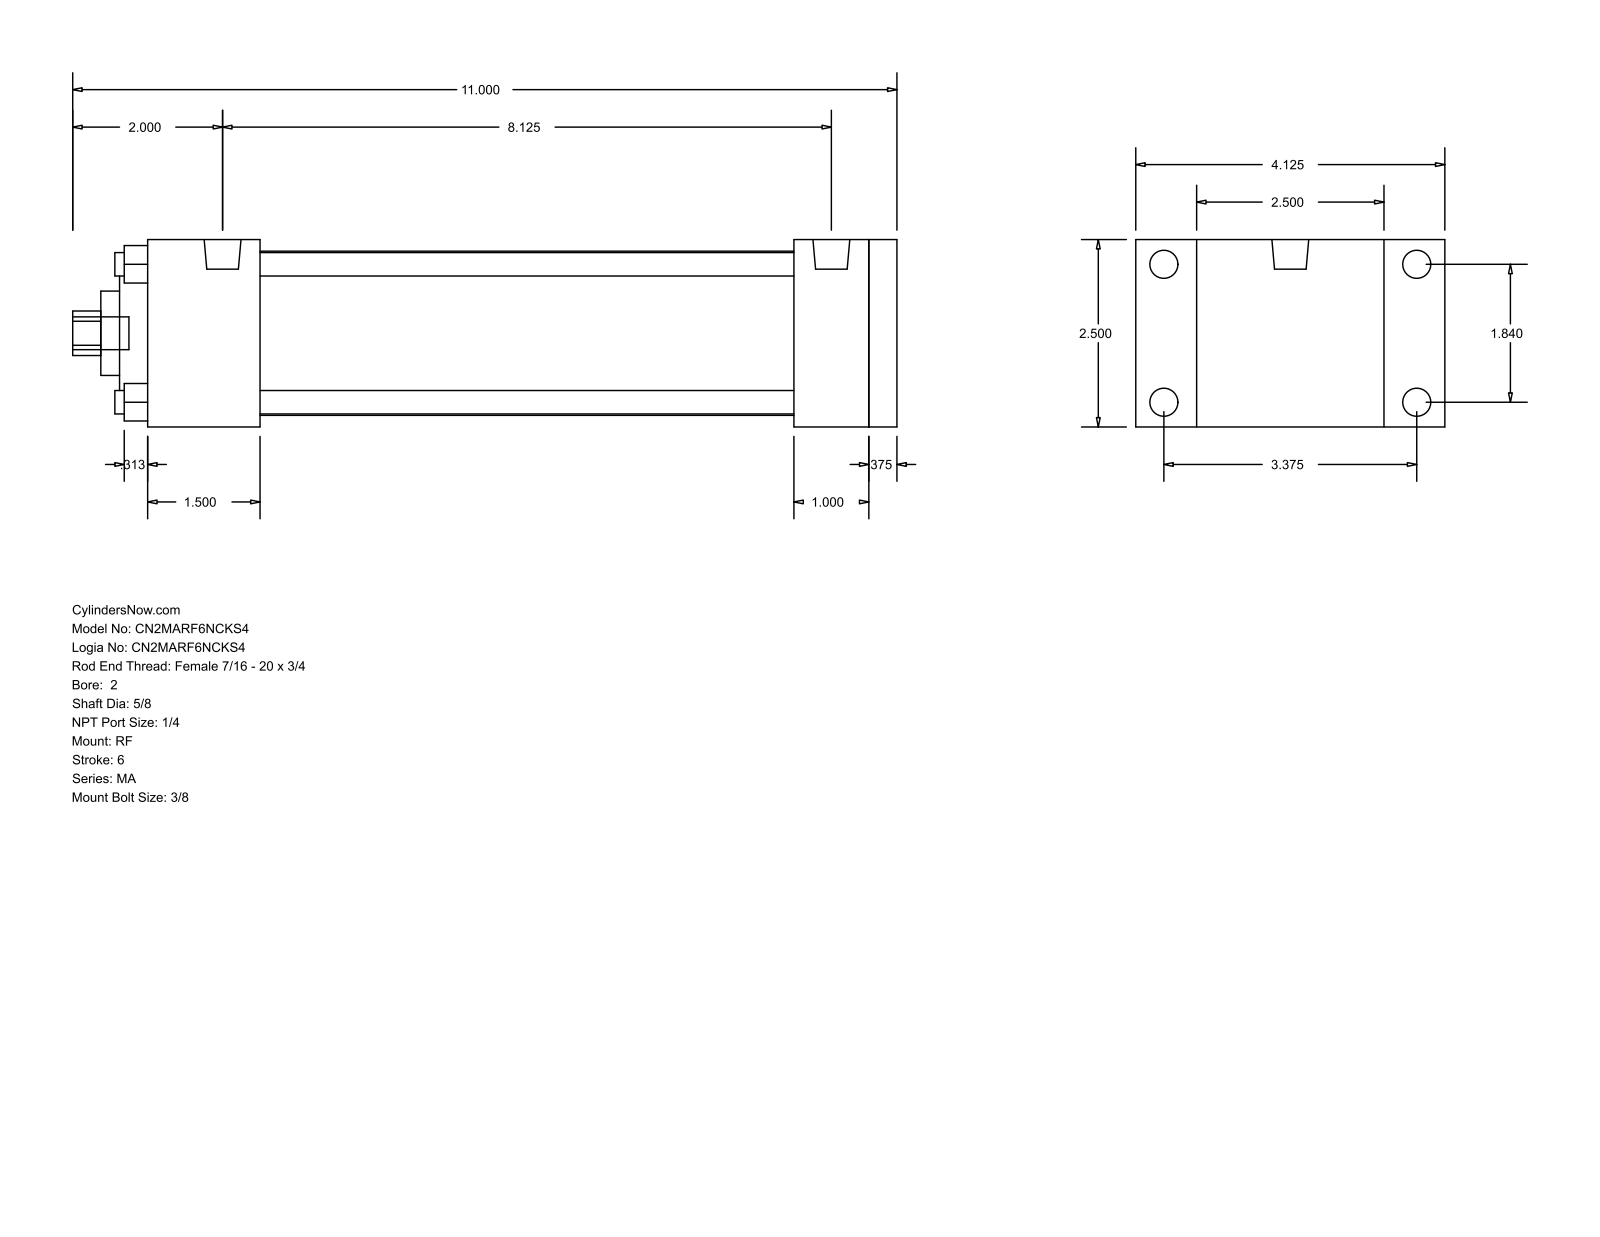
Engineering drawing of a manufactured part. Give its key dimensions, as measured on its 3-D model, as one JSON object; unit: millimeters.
{"part_name": "MA_RF__0200_0.625", "step_written_by": "GSSL Pune (CONFIG_CONTROL_DESIGN)", "units": "millimeters", "bodies": {"solids": 0, "faces": 94, "planar": 65, "cylindrical": 29, "other": 0}, "overall_size": [279.4, 104.78, 63.5], "round_holes": [[7.94, 4], [15.88, 1], [28.57, 1], [50.8, 1], [55.63, 1]], "round_bosses_or_shafts": [[9.53, 4], [7.94, 4], [12.49, 2], [11.11, 1]], "partial_cylinders_radius": [[7.54, 1]], "face_to_face_distances": [63.5, 9.52, 254, 38.1, 244.48, 206.38, 215.9, 219.07, 180.97, 25.41], "hole_center_spacings": [33.05, 46.74, 66.1]}
